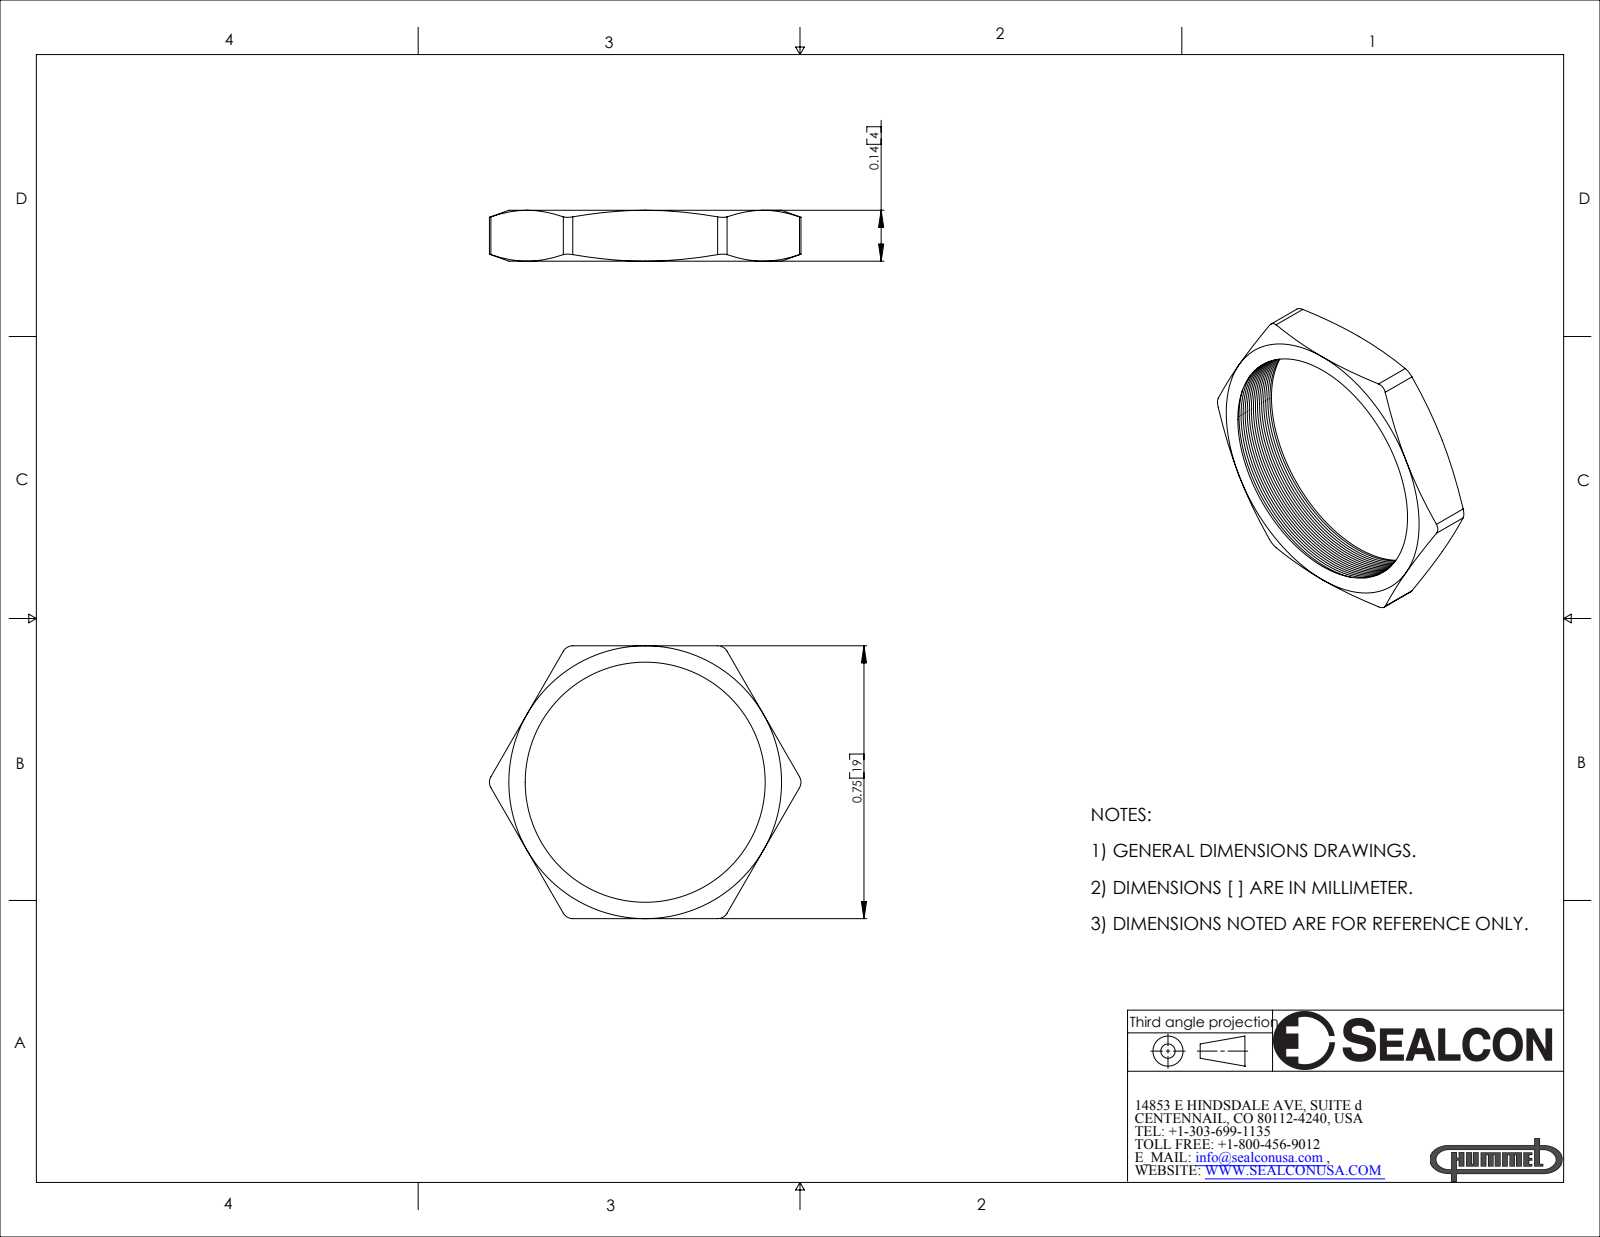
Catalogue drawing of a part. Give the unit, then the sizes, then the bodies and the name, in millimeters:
Units: millimetres
Overall size (bounding box): 21.8 × 19.1 × 3.6
Partial cylindrical surfaces — rounded edges, fillets, slot ends (radius × count): R0.8 ×6
Main face-to-face distances: 19.1, 3.6, 19.1
Volume: 260 mm³ · Surface area: 775 mm²
Bodies: 1 solid, 97 faces (8 planar, 7 cylindrical, 82 other)
Part name (STEP PRODUCT): NN-09-BR
STEP written by: SolidWorks 2007 (CONFIG_CONTROL_DESIGN)
